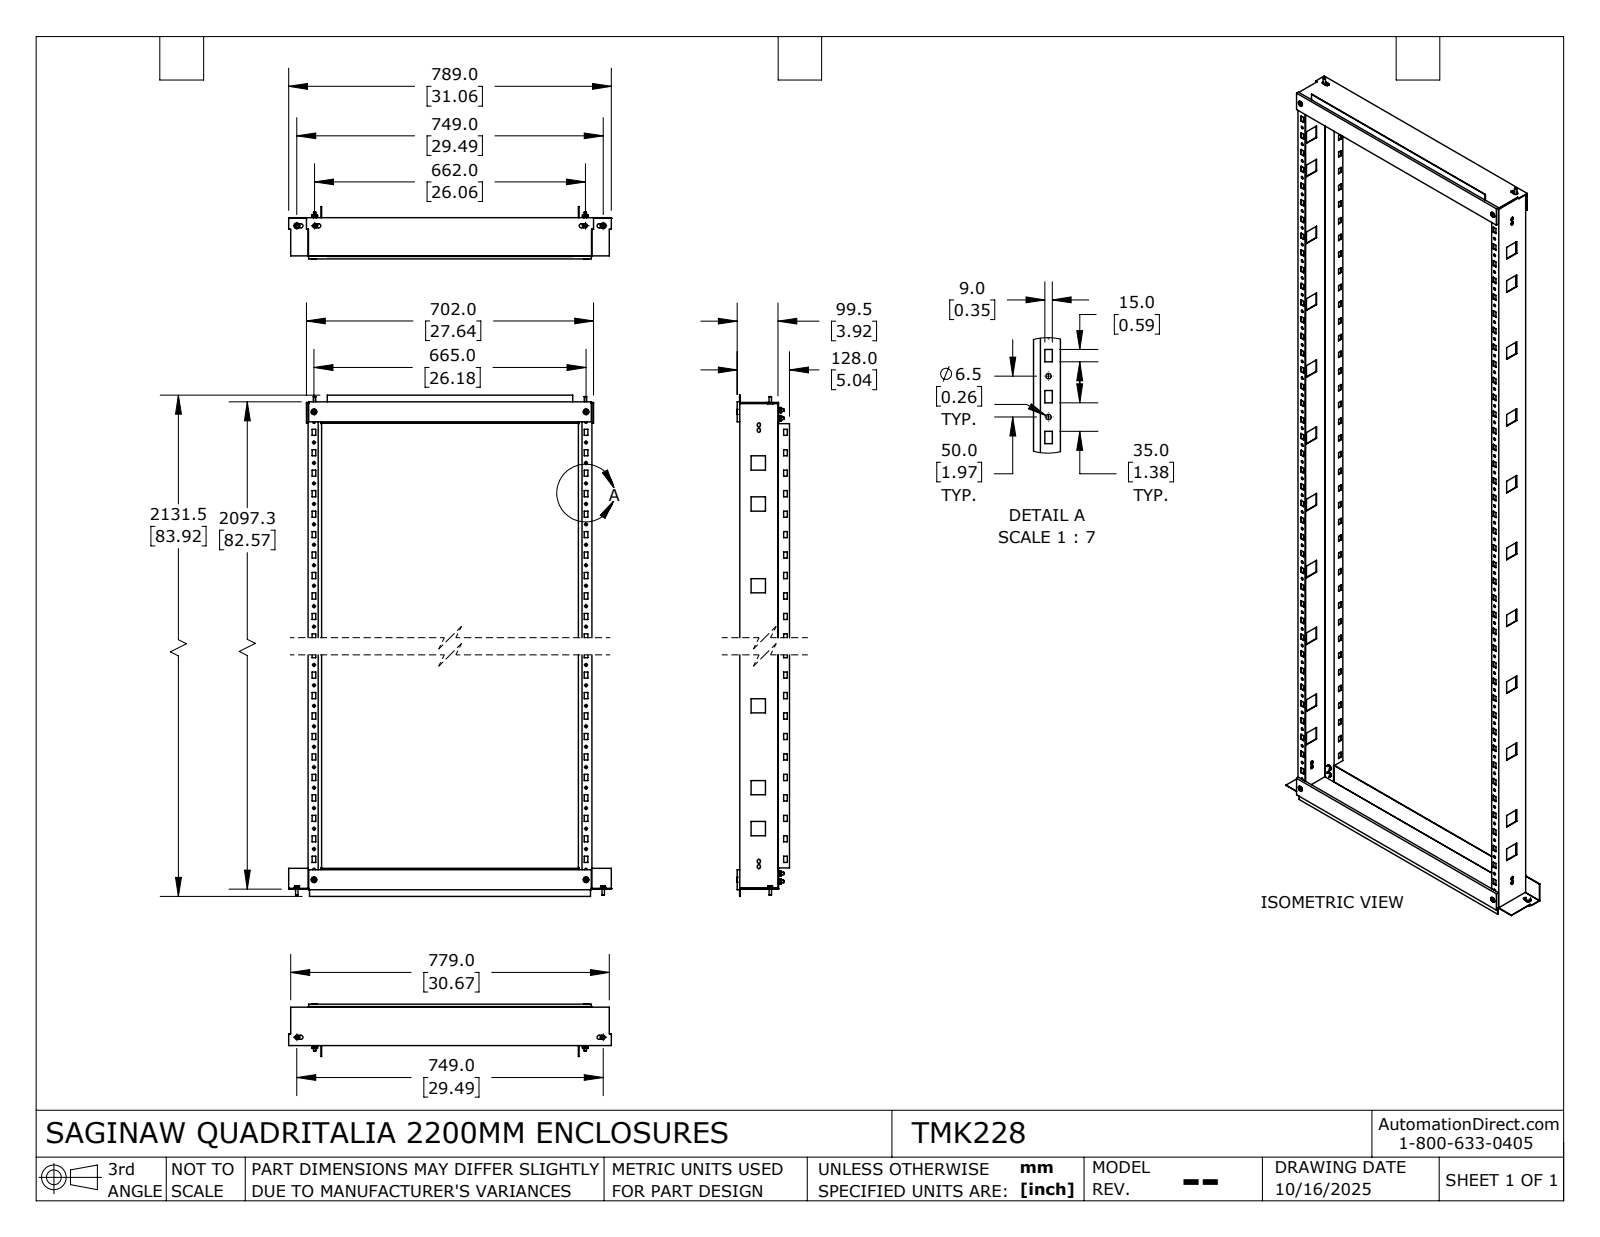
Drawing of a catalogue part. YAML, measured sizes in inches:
part_name: "TMK228"
step_written_by: "SolidWorks 2024 (AUTOMOTIVE_DESIGN)"
units: inches
bodies: {solids: 1, faces: 2466, planar: 1688, cylindrical: 638, other: 140}
overall_size: [83.917, 31.063, 5.051]
volume: 92.34
surface_area: 3154
round_holes:
  - {diameter: 0.256, count: 82}
  - {diameter: 0.276, count: 8}
  - {diameter: 0.156, count: 4}
round_bosses_or_shafts:
  - {diameter: 0.236, count: 16}
  - {diameter: 0.551, count: 12}
  - {diameter: 0.472, count: 4}
  - {diameter: 0.394, count: 4}
partial_cylinders:
  - {radius: 0.01, count: 96}
  - {radius: 0.02, count: 80}
  - {radius: 0.039, count: 32}
  - {radius: 0.138, count: 24}
  - {radius: 0.177, count: 16}
  - {radius: 0.197, count: 8}
face_to_face_distances: [0.059, 27.264, 26.024, 1.24, 27.323, 27.205, 3.602, 3.661, 0.256, 3.917]
hole_center_spacings: [3.937, 7.874, 11.811, 15.748, 1.969, 19.685, 5.906, 9.843]
